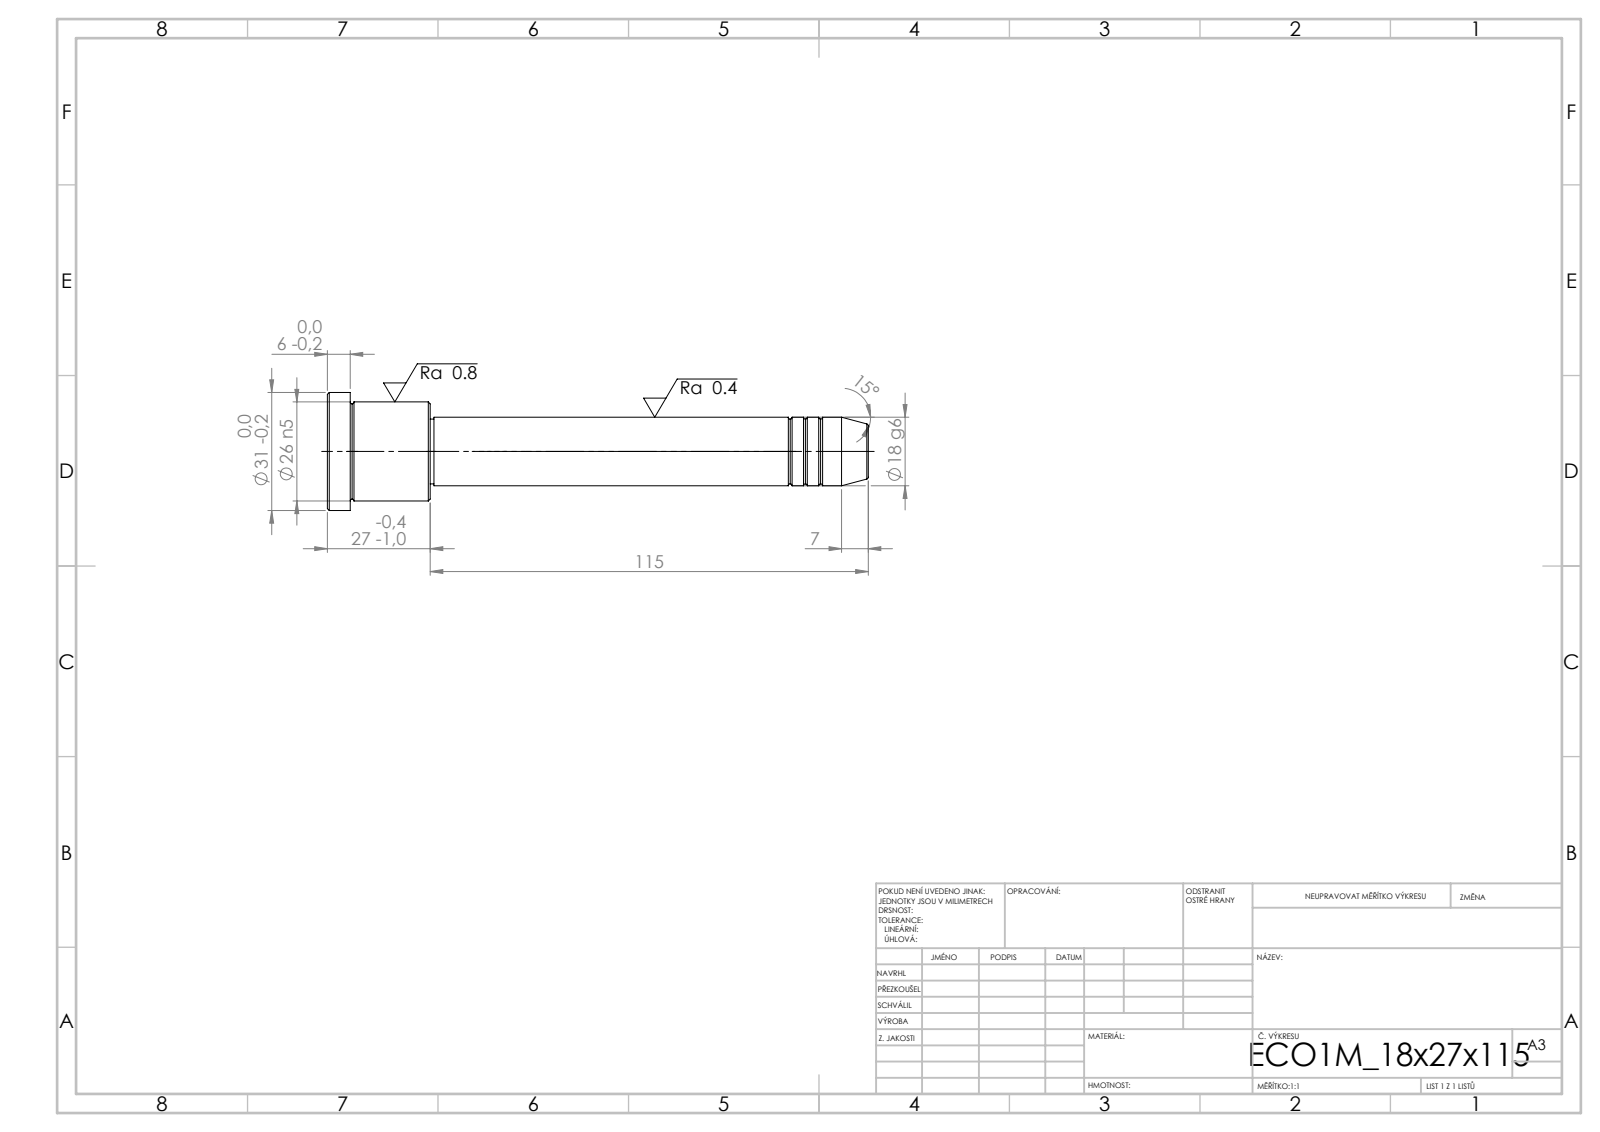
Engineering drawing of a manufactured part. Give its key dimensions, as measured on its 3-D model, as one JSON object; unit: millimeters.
{"step_written_by": "SolidWorks 2019 (CONFIG_CONTROL_DESIGN)", "units": "millimeters", "bodies": {"solids": 1, "faces": 43, "planar": 5, "cylindrical": 14, "other": 24}, "overall_size": [142, 31, 31], "volume_mm3": 44449, "surface_area_mm2": 10313, "round_bosses_or_shafts": [[31, 1], [26, 1], [18, 1], [17, 1]], "face_to_face_distances": [27, 21, 6, 115, 136, 142, 114, 1, 22, 28]}
